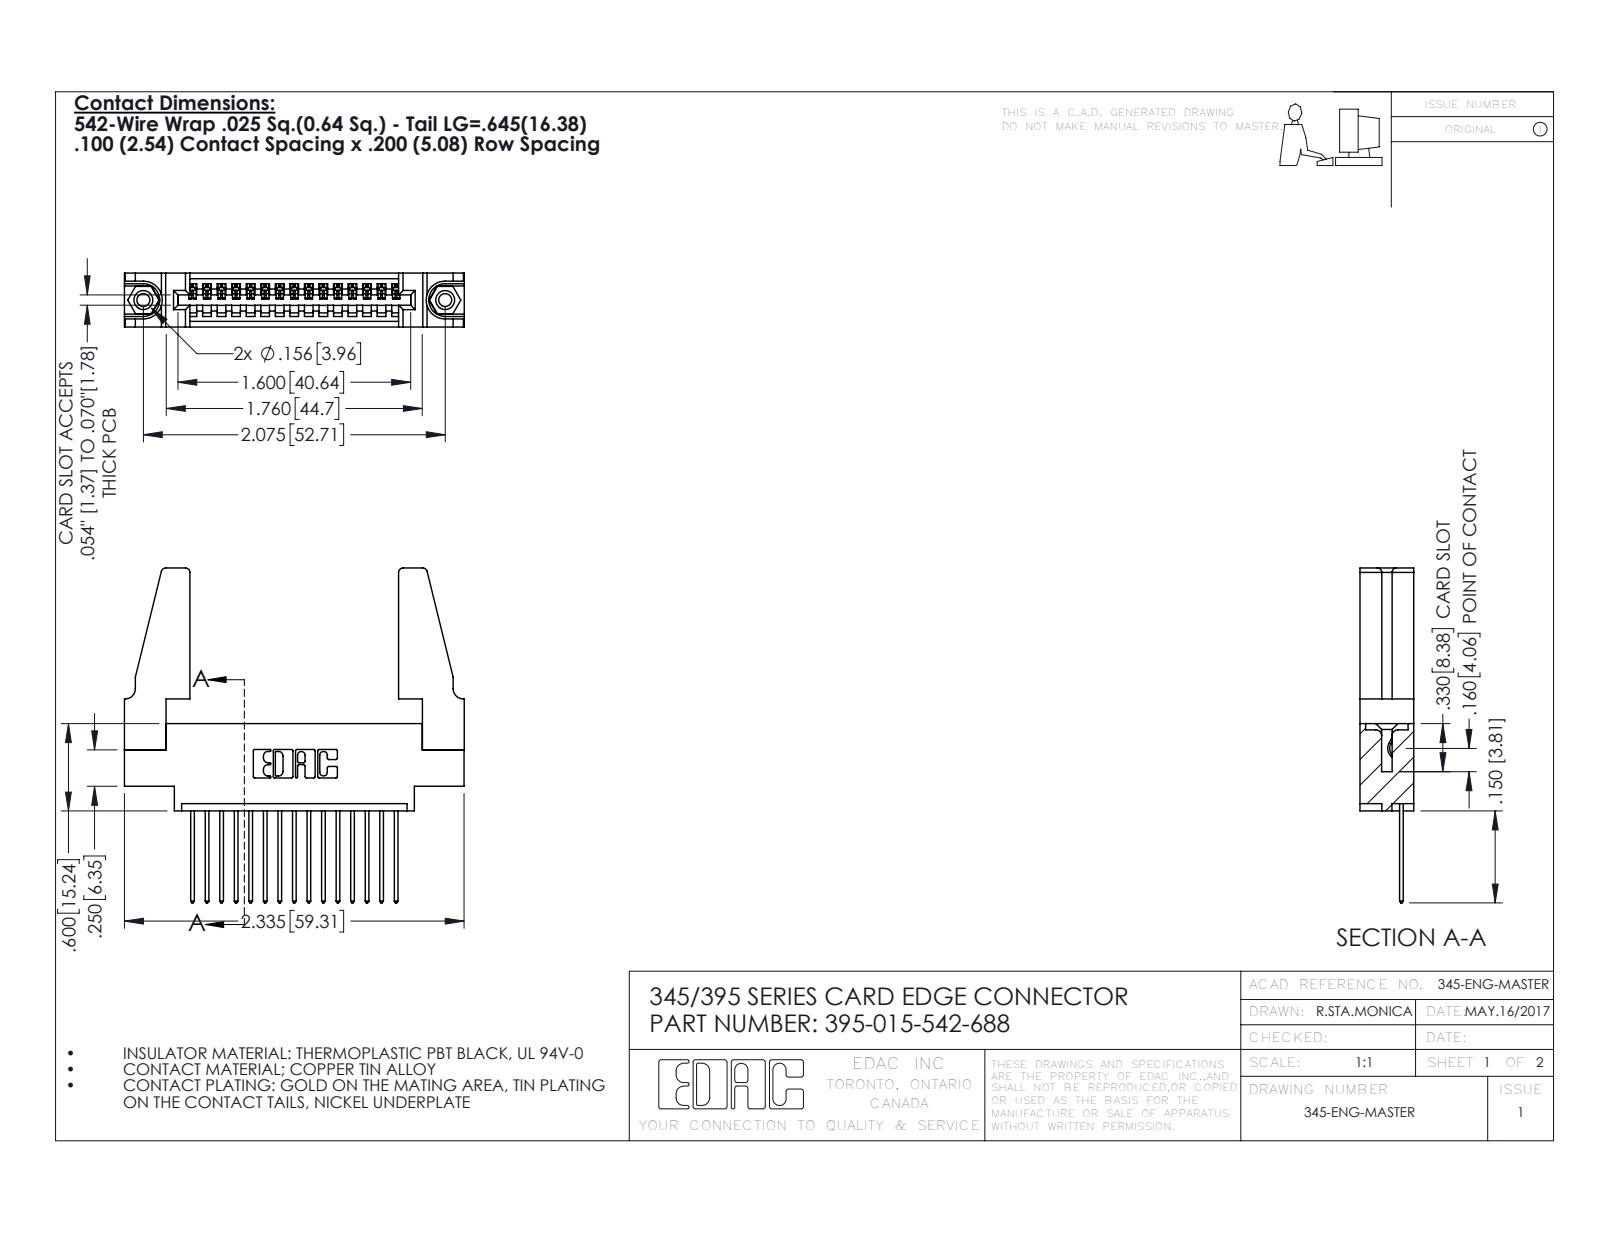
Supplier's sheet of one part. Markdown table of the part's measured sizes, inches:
| quantity | value |
| --- | --- |
| part name | 345-220-078_345-220-088; 345-250-001_345-250-001-102; 345 Part_0.170 Offset - 0.156 Dia-TH; 345-292-001_345-293-142 (+1 more) |
| STEP written by | SolidWorks 2016 (CONFIG_CONTROL_DESIGN) |
| units | inches |
| bodies | 20 solids, 1124 faces (756 planar, 352 cylindrical, 16 other) |
| overall size | 2.336 × 2.302 × 0.37 |
| volume | 0.524 in³ |
| surface area | 15.79 in² |
| round holes (diameter × count) | 0.089 × 2, 0.125 × 2, 0.156 × 2, 0.064 × 1 |
| round bosses / shafts (diameter × count) | 0.155 × 2 |
| partial cylindrical surfaces (radius × count) | 0.006 × 30, 0.01 × 30, 0.01 × 22, 0.03 × 8, 0.007 × 6, 0.031 × 6, 0.026 × 3, 0.031 × 2 |
| main face-to-face distances | 0.37, 0.072, 0.298, 0.098, 0.272, 0.025, 0.2, 0.225, 0.148, 0.15 |
| hole center spacings | 0.27, 1.842, 2.075 |
